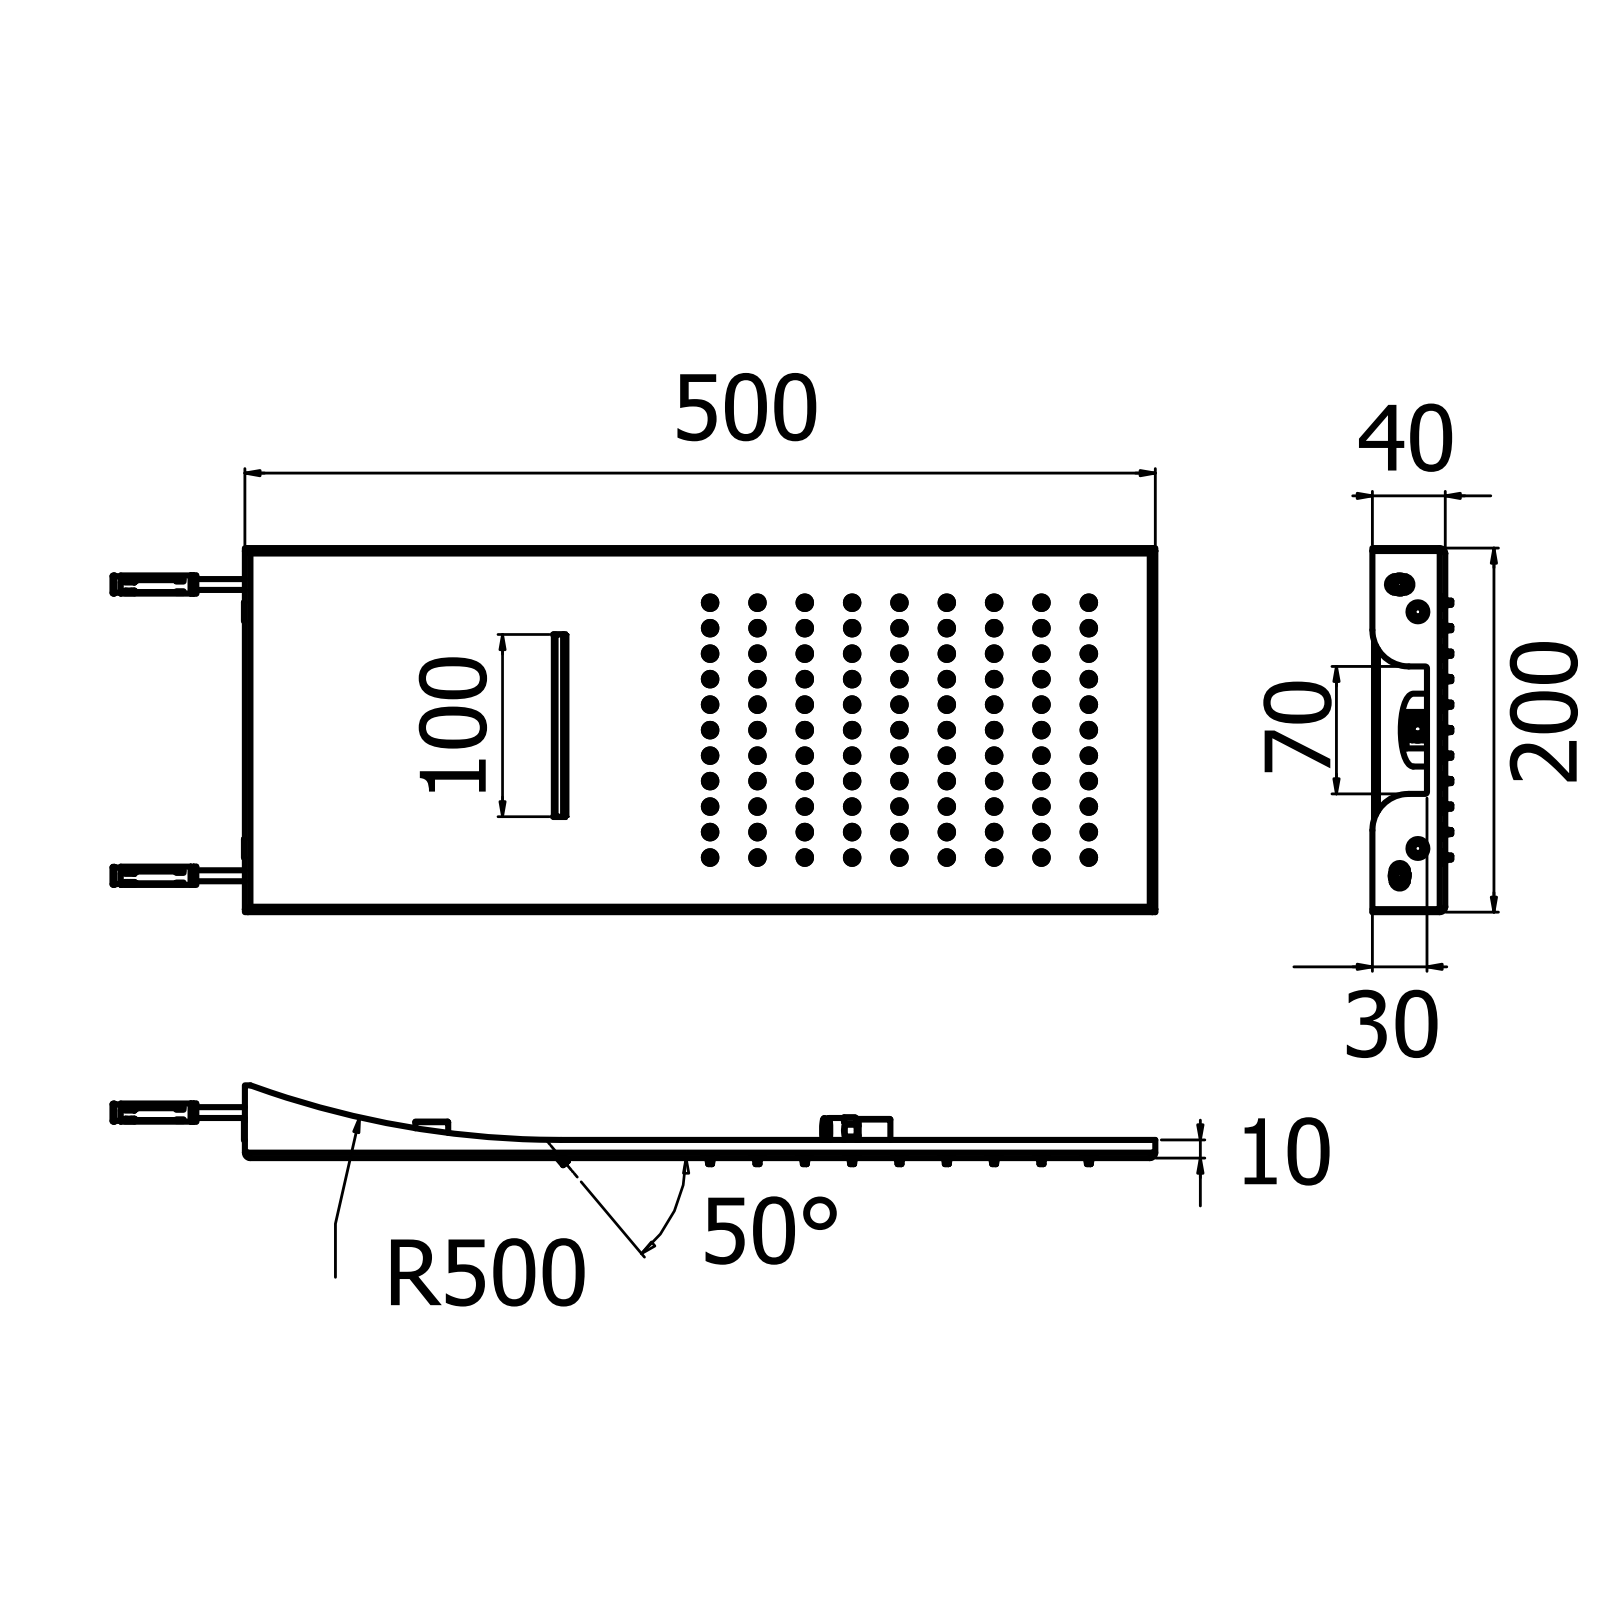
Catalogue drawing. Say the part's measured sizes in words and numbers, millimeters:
The part is named "22280 <3501>; S.01006 <3516>; Importato 10; Importato 12 (+7 more)". Its 3-D file was written by "Shapr3D (AUTOMOTIVE_DESIGN)". It is 3 solids with 2788 faces: 848 planar, 773 cylindrical and 1167 other. Overall it measures 572.7 by 200 by 43.89 millimeters. Its volume is 422 151 cubic millimeters and its surface area 573 432 square millimeters. Round holes: 103 of diameter 5, 99 of diameter 1.5, 99 of diameter 1.7, 10 of diameter 6, 10 of diameter 6.2, 3 of diameter 3.2, 2 of diameter 2.5, 2 of diameter 6.5, 2 of diameter 8, 2 of diameter 8.4, 2 of diameter 8.57, 2 of diameter 14.1. Round bosses or shafts: 101 of diameter 10, 6 of diameter 4.3, 6 of diameter 3, 3 of diameter 13.9, 3 of diameter 6.7, 2 of diameter 20, 2 of diameter 11.5, 2 of diameter 10.4. Partial cylindrical surfaces (rounded edges, fillets, slot ends): 78 of radius 0.1, 62 of radius 2, 34 of radius 1, 26 of radius 0.2, 8 of radius 3.2, 6 of radius 20, 4 of radius 1.5, 4 of radius 3. The main face-to-face distances are 1, 4, 3, 1.5, 7, 8.5, 2.5, 9.5, 2, 5. The hole center spacings are 38.21, 26, 53.85, 59.06, 29.53, 76.42, 49.4, 61.74.
